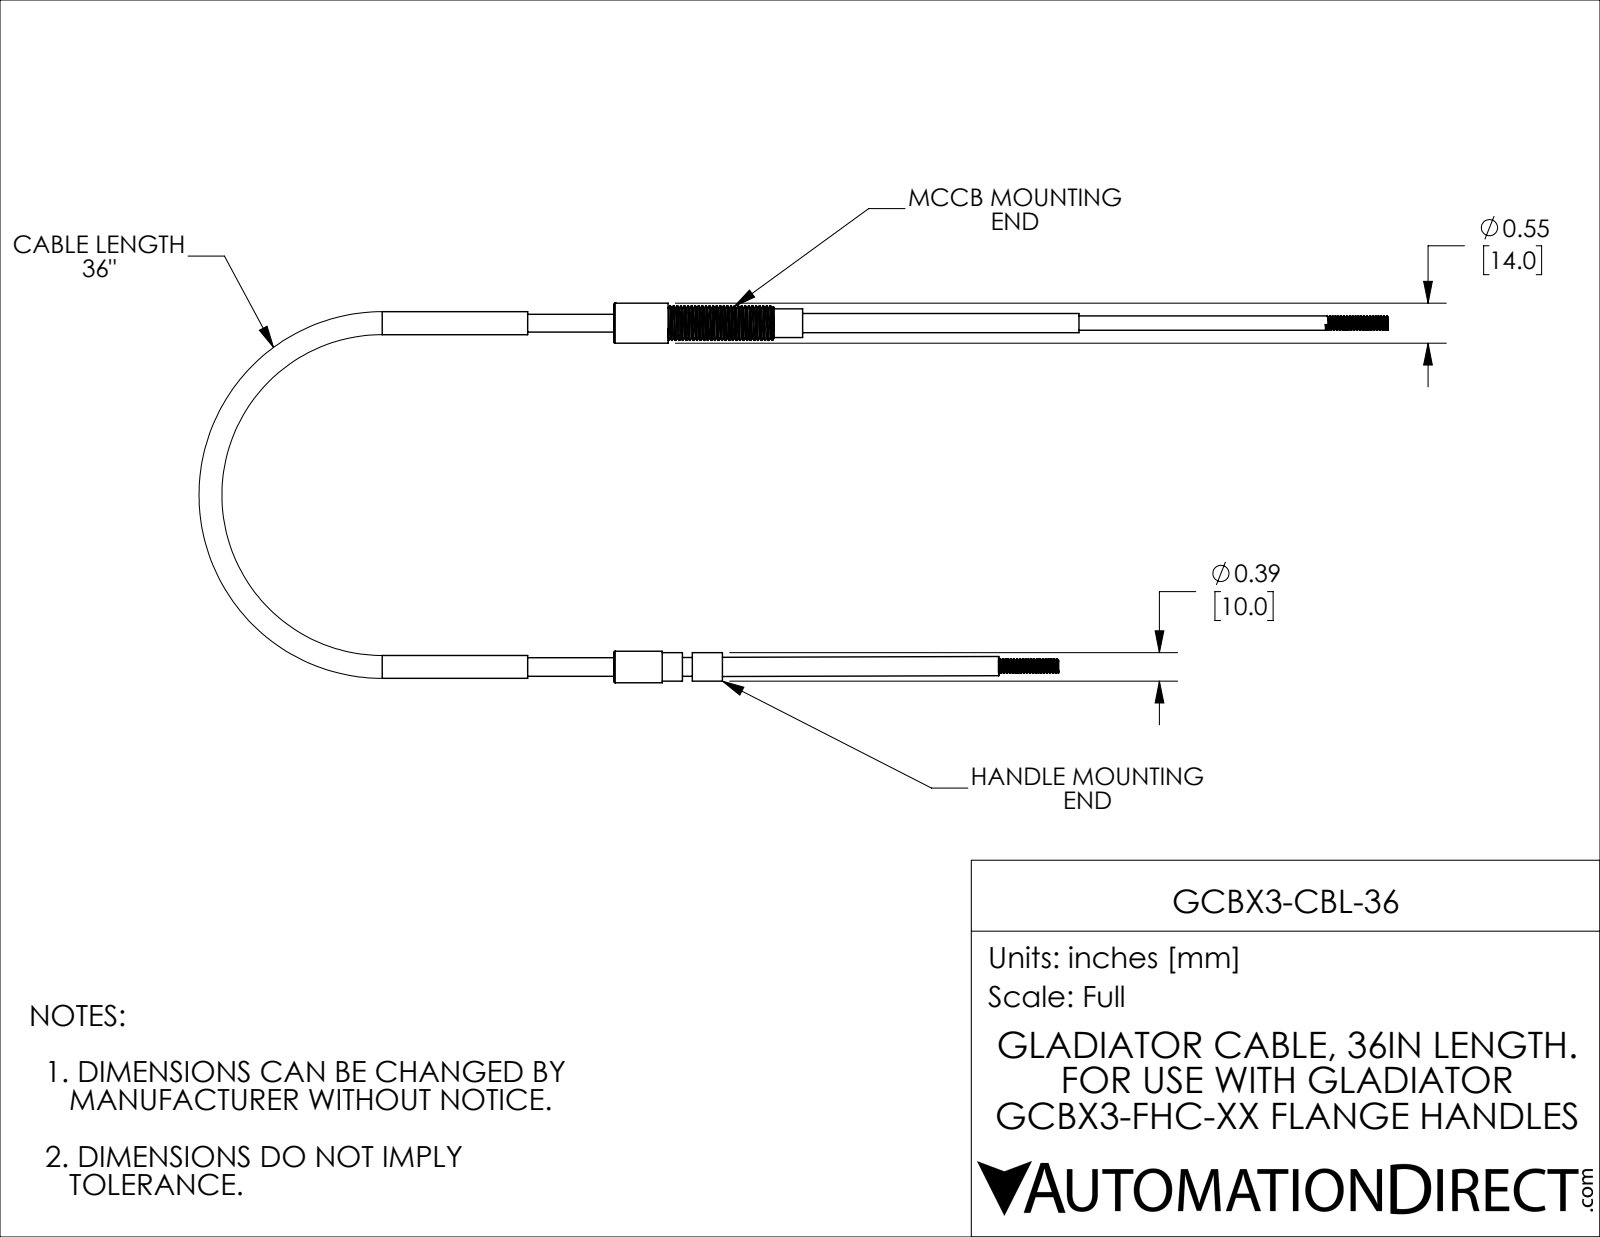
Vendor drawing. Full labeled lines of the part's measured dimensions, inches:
Part name (STEP PRODUCT): GCBX3-CBL-36_2; GCBX3-CBL-36_1; GCBX3-CBL-36
STEP written by: SolidWorks 2021 (CONFIG_CONTROL_DESIGN)
Units: inches
Bodies: 9 solids, 262 faces (29 planar, 181 cylindrical, 52 other)
Overall size (bounding box): 13.831 × 5.217 × 0.551
Volume: 1.509 in³ · Surface area: 33.17 in²
Round holes (diameter × count): ⌀0.201 ×2, ⌀0.118 ×1, ⌀0.315 ×1
Round bosses / shafts (diameter × count): ⌀0.394 ×2, ⌀0.264 ×2, ⌀0.197 ×2, ⌀0.551 ×1, ⌀0.472 ×1, ⌀0.433 ×1, ⌀0.315 ×1, ⌀0.287 ×1
Main face-to-face distances: 1.181, 3.181, 2, 2.598, 3.78, 5.78, 0.748, 1.85, 1.929, 0.413
